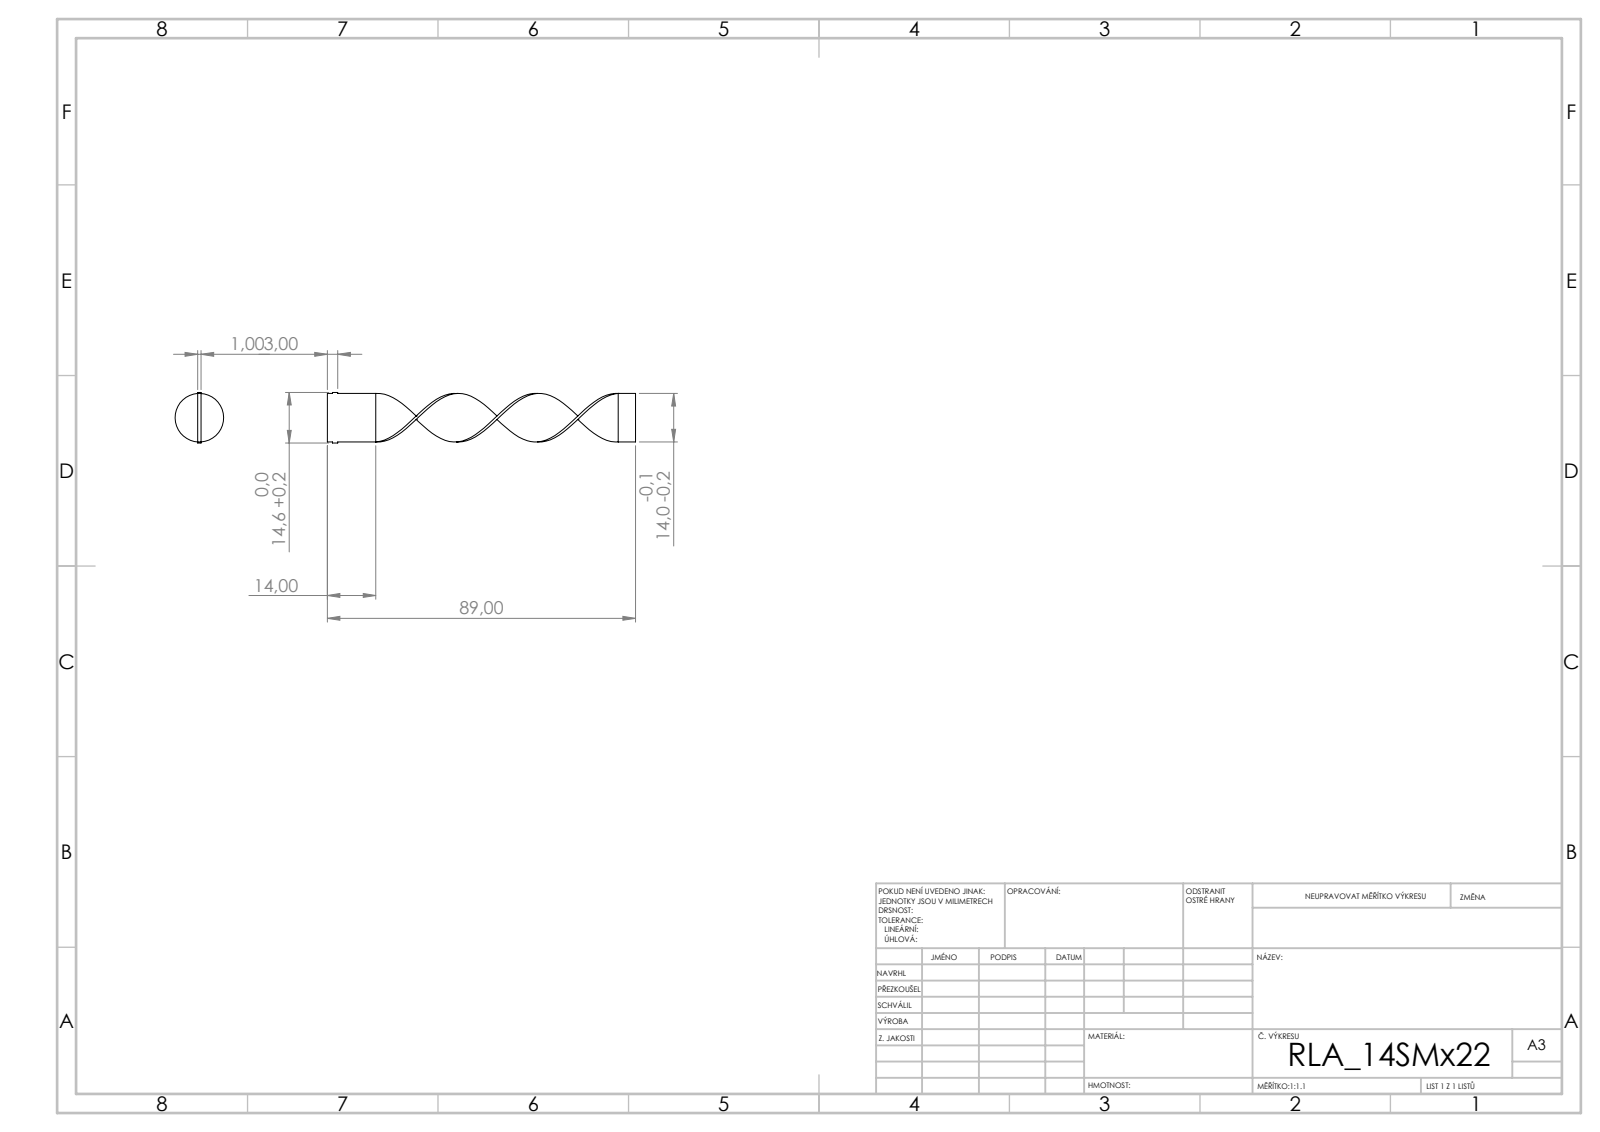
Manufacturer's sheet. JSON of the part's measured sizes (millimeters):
{"step_written_by": "SolidWorks 2019 (CONFIG_CONTROL_DESIGN)", "units": "millimeters", "bodies": {"solids": 1, "faces": 22, "planar": 18, "cylindrical": 0, "other": 4}, "overall_size": [89, 14.6, 14.04], "volume_mm3": 1247, "surface_area_mm2": 2963, "face_to_face_distances": [1, 14, 89, 14.3, 14.6, 1.5, 86, 87.5, 3]}
